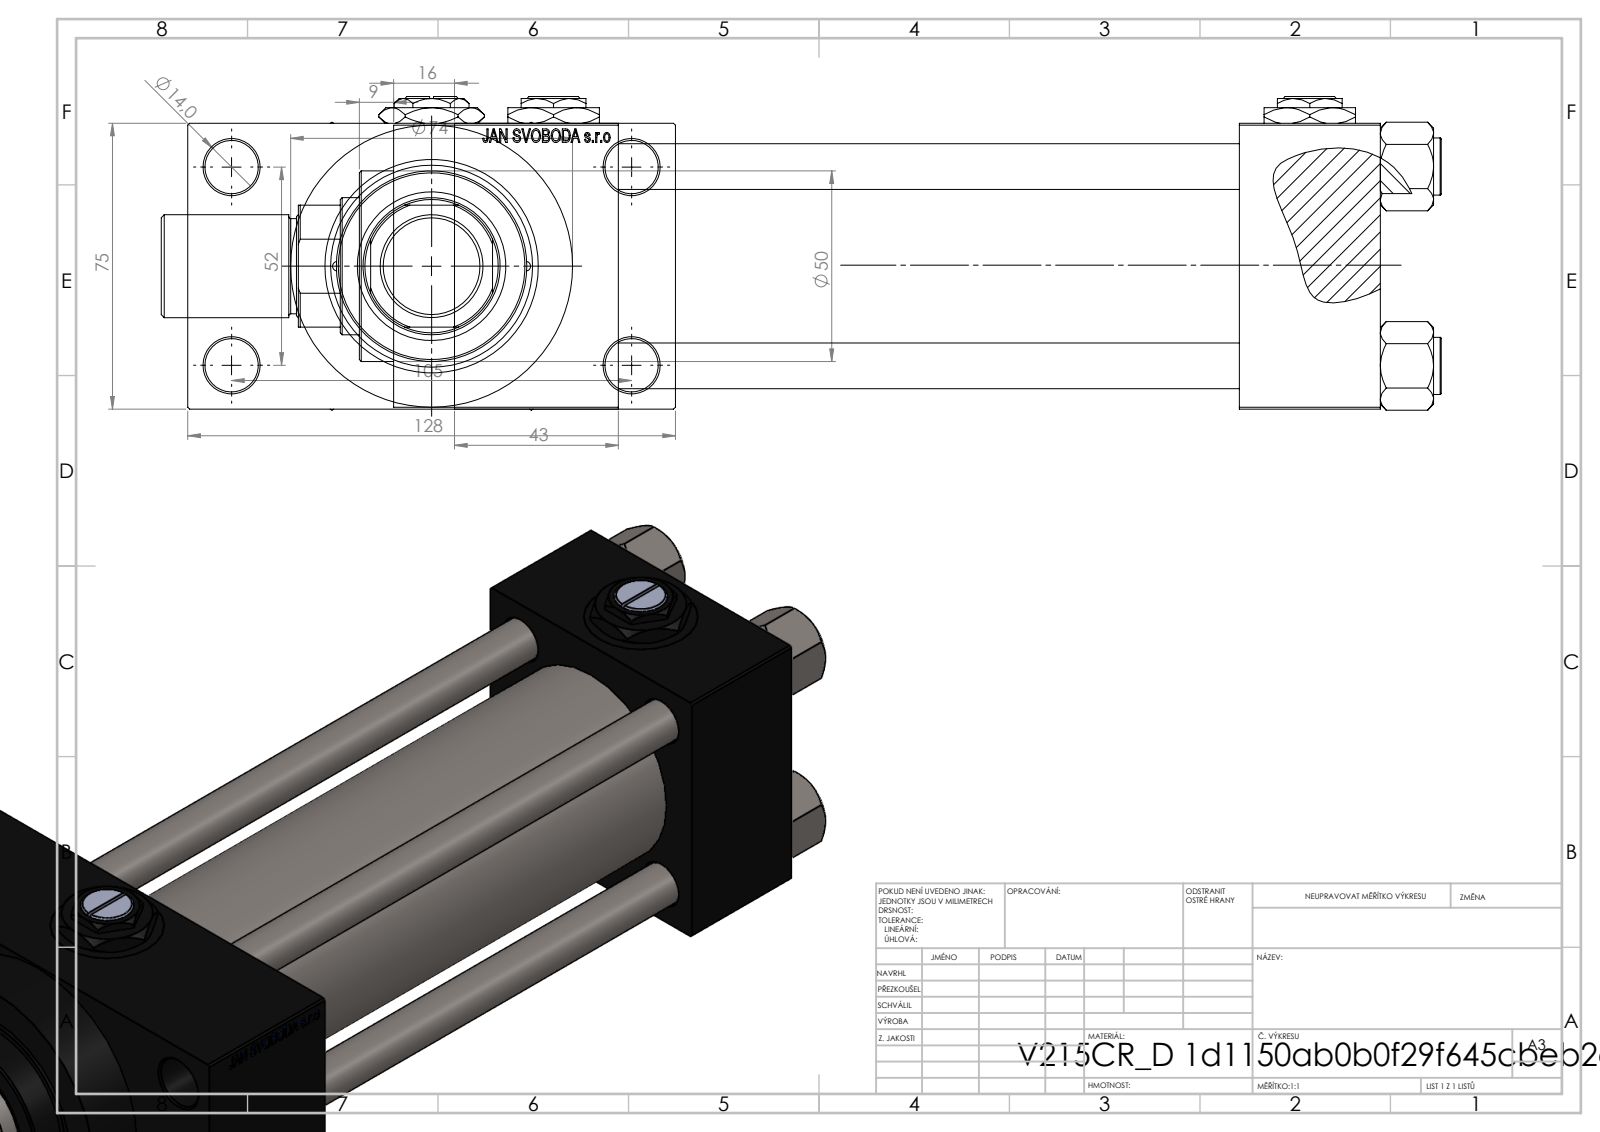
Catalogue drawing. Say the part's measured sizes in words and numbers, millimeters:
The part is named "V215CR_D_TYCINKA; V215_VC_A; NUT_M5_D; ROD_END_AH (+3 more)". Its 3-D file was written by "SolidWorks 2019 (CONFIG_CONTROL_DESIGN)". It is 14 solids with 1228 faces: 553 planar, 107 cylindrical and 568 other. Overall it measures 336 by 128 by 82.27 millimeters. Its volume is 1 040 000 cubic millimeters and its surface area 246 655 square millimeters. Round holes: 4 of diameter 12, 4 of diameter 14, 4 of diameter 20.96, 4 of diameter 30, 3 of diameter 7, 2 of diameter 2.5, 1 of diameter 25.5, 1 of diameter 36, 1 of diameter 39, 1 of diameter 41, 1 of diameter 53. Round bosses or shafts: 4 of diameter 15, 1 of diameter 74, 1 of diameter 56, 1 of diameter 50, 1 of diameter 27, 1 of diameter 25. Partial cylindrical surfaces (rounded edges, fillets, slot ends): 1 of radius 17.5. The main face-to-face distances are 75, 163, 37, 200, 26.5, 243, 43, 206, 101.5, 16. The hole center spacings are 26.19, 26.35, 36.98, 38.03, 52.3, 57.22, 58.43, 58.59.
